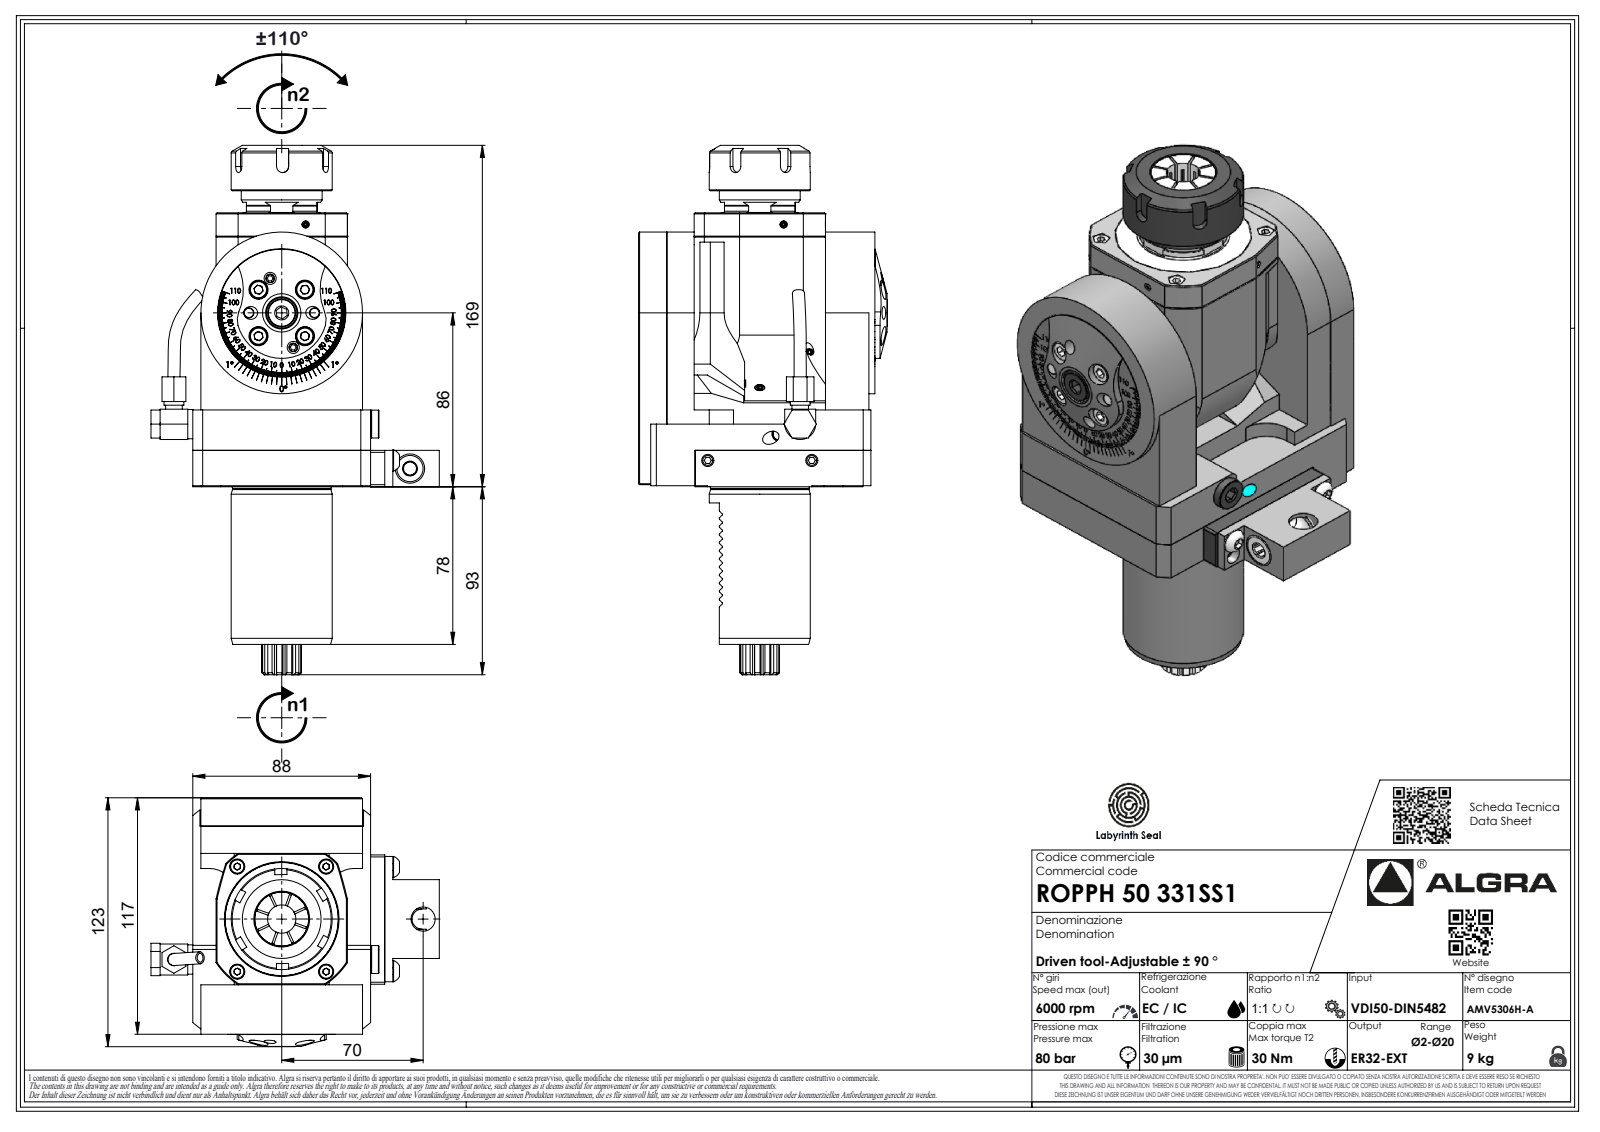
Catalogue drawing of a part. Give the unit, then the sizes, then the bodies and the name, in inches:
Units: inches
Overall size (bounding box): 10.311 × 5.618 × 4.843
Round holes (diameter × count): ⌀0.083 ×1
Round bosses / shafts (diameter × count): ⌀3.15 ×1, ⌀1.969 ×1, ⌀1.917 ×1, ⌀1.575 ×1, ⌀0.571 ×1, ⌀0.386 ×1, ⌀0.323 ×1, ⌀0.251 ×1
Partial cylindrical surfaces — rounded edges, fillets, slot ends (radius × count): R0.369 ×24, R0.012 ×12, R0.013 ×7, R0.02 ×7, R0.146 ×7, R0.118 ×5, R0.039 ×4, R0.394 ×2
Main face-to-face distances: 0.157, 2.559, 3.307, 0.02, 3.012, 0.453, 0.886, 1.083, 0.295, 2.854
Volume: 78.11 in³ · Surface area: 173.7 in²
Bodies: 1 solid, 677 faces (382 planar, 142 cylindrical, 153 other)
Part name (STEP PRODUCT): ROPPH50331SS1
STEP written by: SolidWorks 2023 (AUTOMOTIVE_DESIGN)
